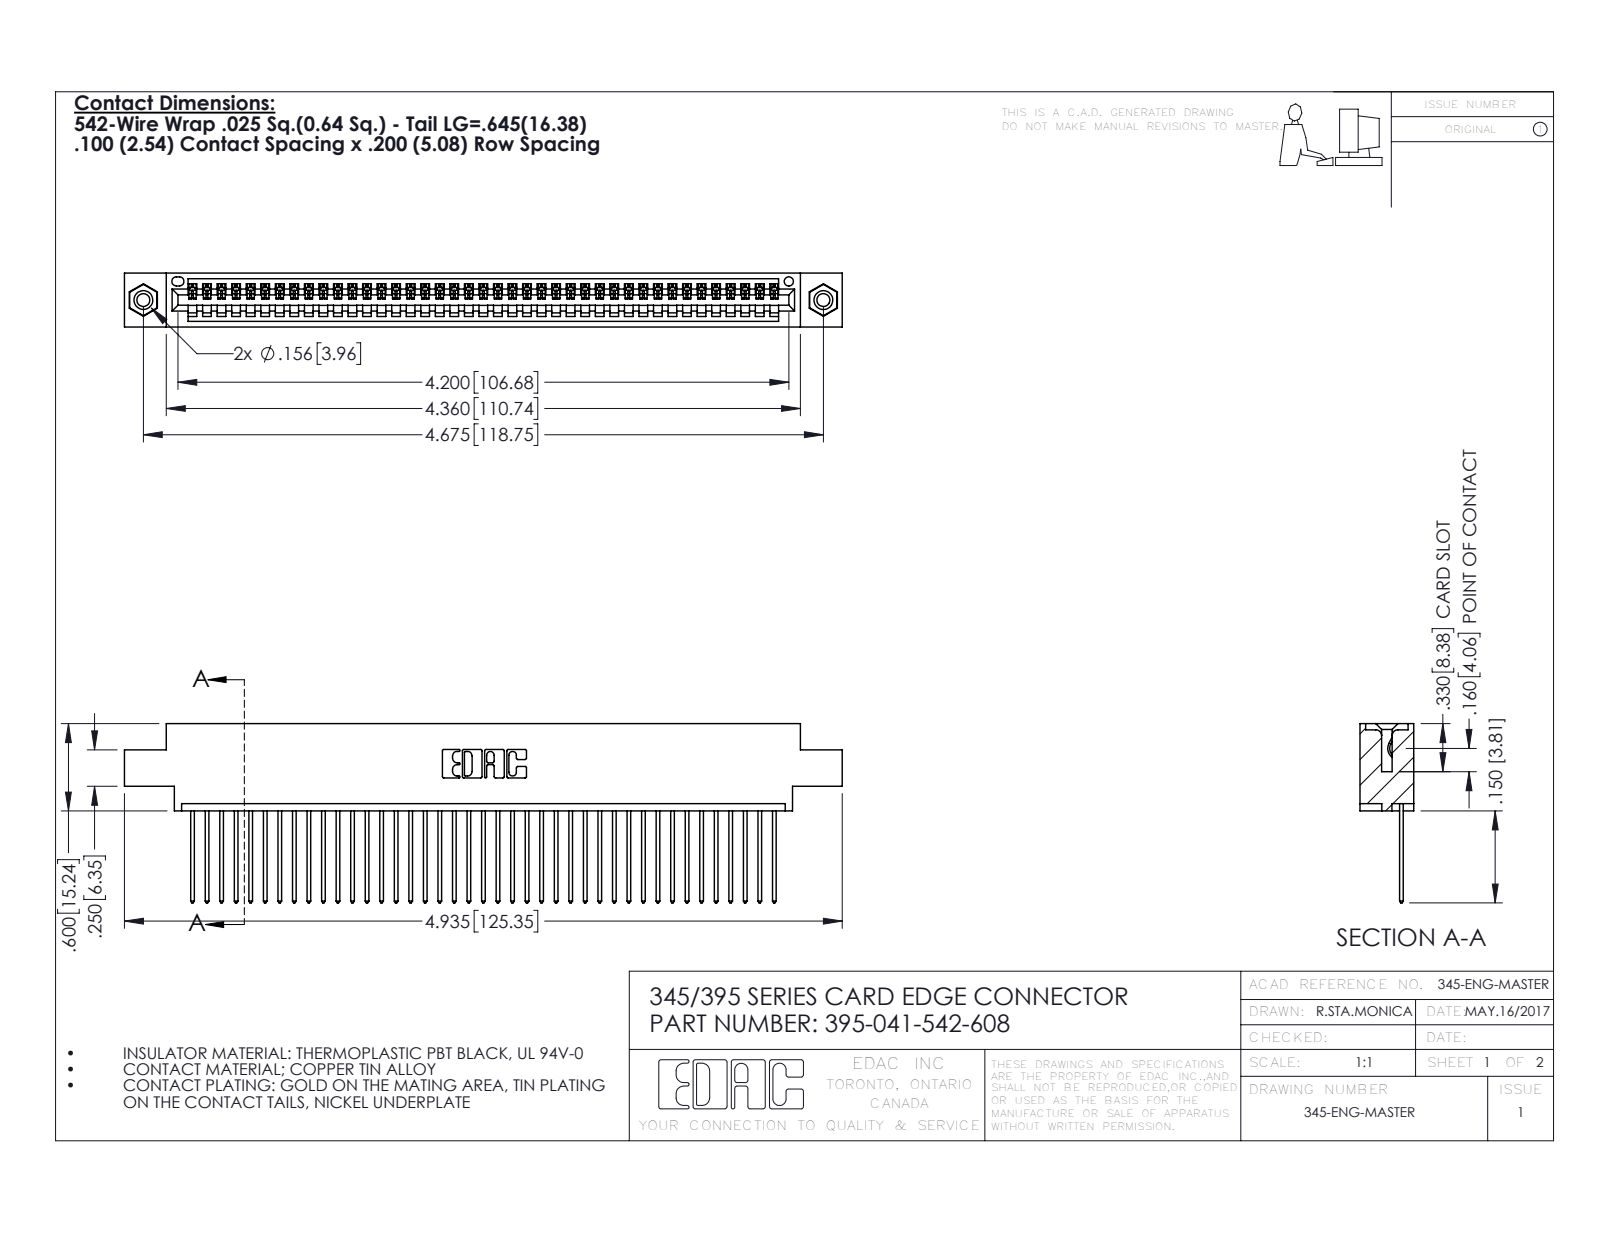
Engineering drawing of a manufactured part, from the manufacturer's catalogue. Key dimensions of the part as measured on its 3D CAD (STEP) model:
Part name (STEP PRODUCT): 395-041-542-608; 345 Part_0.170 Offset - 0.156 Dia-TI; 345-250-001_345-250-003-102; 345-292-001_345-293-142
STEP written by: SolidWorks 2016 (CONFIG_CONTROL_DESIGN)
Units: inches
Bodies: 44 solids, 2568 faces (1756 planar, 796 cylindrical, 16 other)
Overall size (bounding box): 4.935 × 1.232 × 0.37
Volume: 0.724 in³ · Surface area: 25.55 in²
Round holes (diameter × count): ⌀0.089 ×2, ⌀0.125 ×2, ⌀0.156 ×2, ⌀0.064 ×1
Round bosses / shafts (diameter × count): ⌀0.155 ×2
Partial cylindrical surfaces — rounded edges, fillets, slot ends (radius × count): R0.006 ×82, R0.01 ×82, R0.01 ×22, R0.007 ×6, R0.031 ×6, R0.026 ×3, R0.031 ×2, R0.04 ×2
Main face-to-face distances: 0.072, 0.298, 0.37, 0.098, 0.272, 0.025, 0.2, 0.225, 0.175, 0.149
Hole centre spacings: 0.27, 4.439, 4.675
